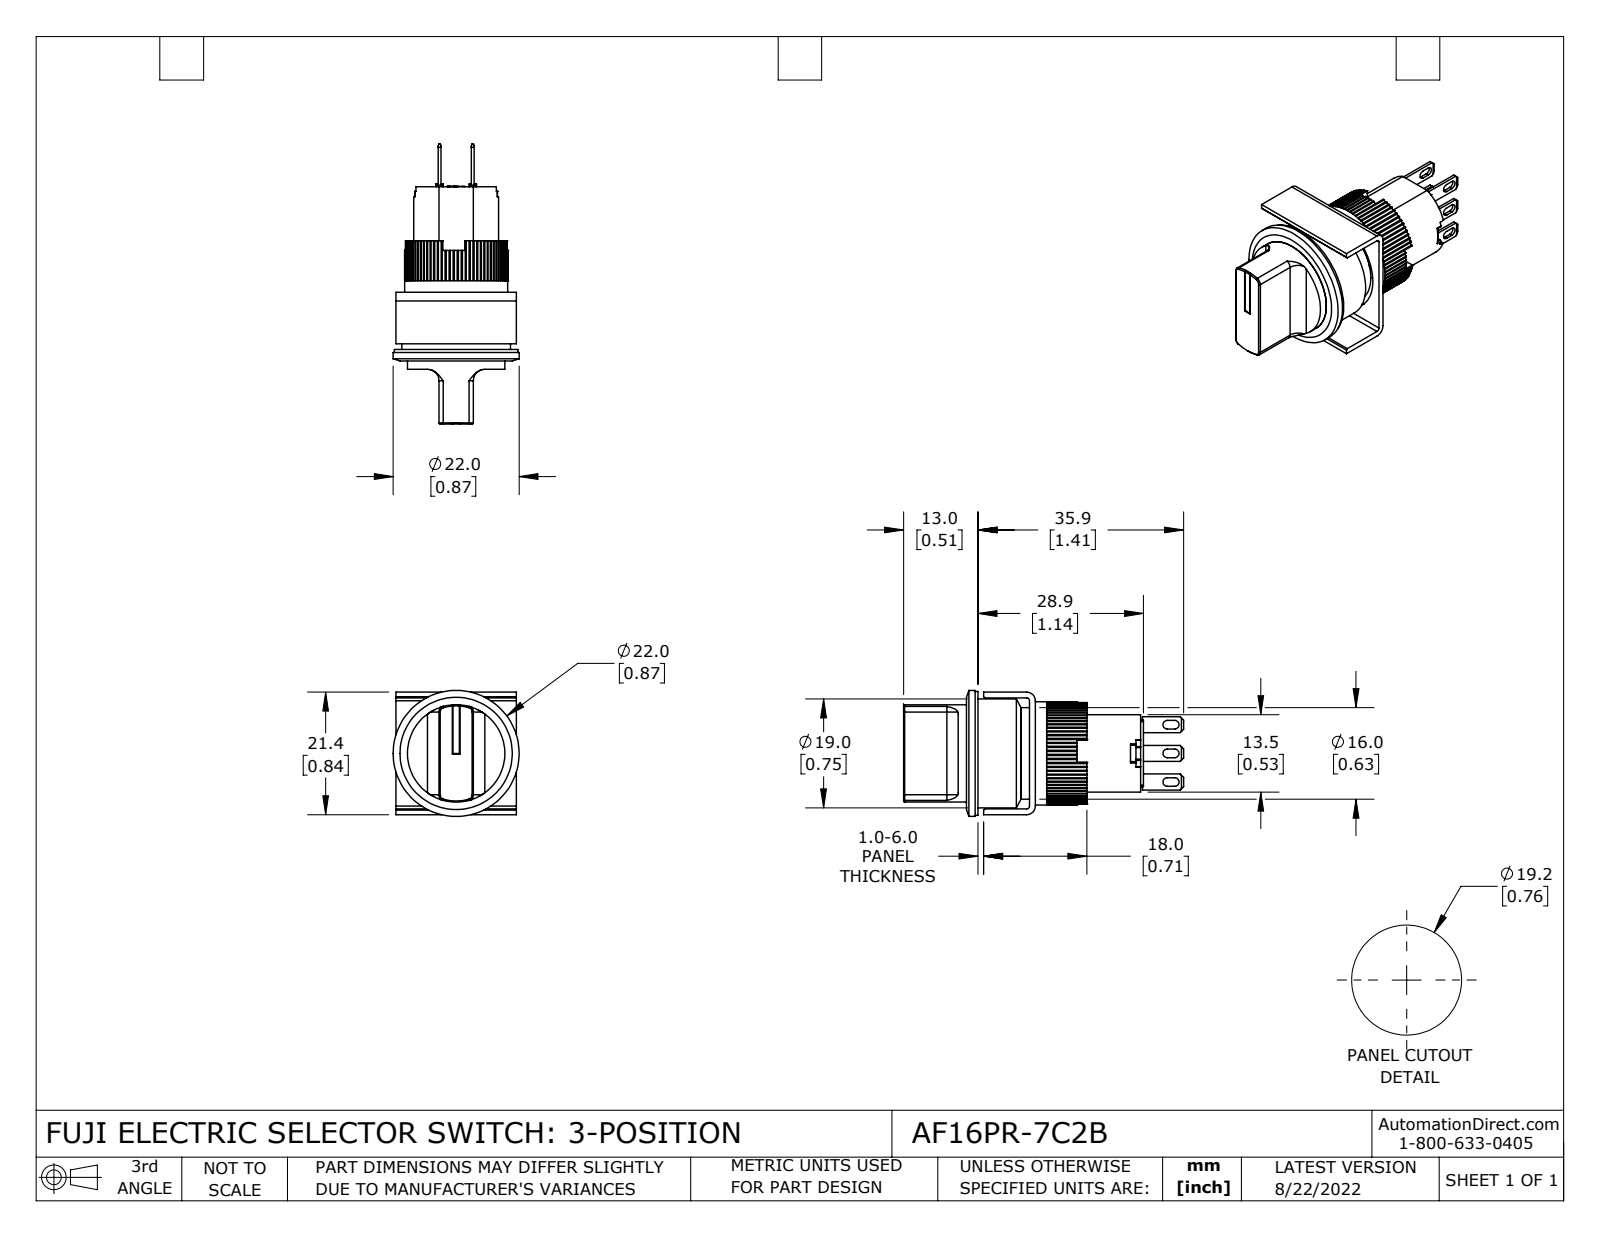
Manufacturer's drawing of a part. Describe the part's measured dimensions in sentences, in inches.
The part is named "AF16PR-7C2B". Its 3-D file was written by "SolidWorks 2021 (CONFIG_CONTROL_DESIGN)". It is 12 solids with 709 faces: 505 planar, 189 cylindrical and 15 other. Overall it measures 1.925 by 0.866 by 0.866 inches. Its volume is 0.493 cubic inches and its surface area 10.41 square inches. Round holes: 1 of diameter 0.039, 1 of diameter 0.669, 1 of diameter 0.709, 1 of diameter 0.748. Round bosses or shafts: 1 of diameter 0.866, 1 of diameter 0.85, 1 of diameter 0.63, 1 of diameter 0.583. Partial cylindrical surfaces (rounded edges, fillets, slot ends): 80 of radius 0.01, 14 of radius 0.008, 6 of radius 0.03, 4 of radius 0.039, 2 of radius 0.02, 2 of radius 0.059, 2 of radius 0.079, 1 of radius 0.331. The main face-to-face distances are 0.374, 0.039, 0.059, 0.803, 0.764, 0.02, 0.433, 0.155, 0.648, 0.232.
